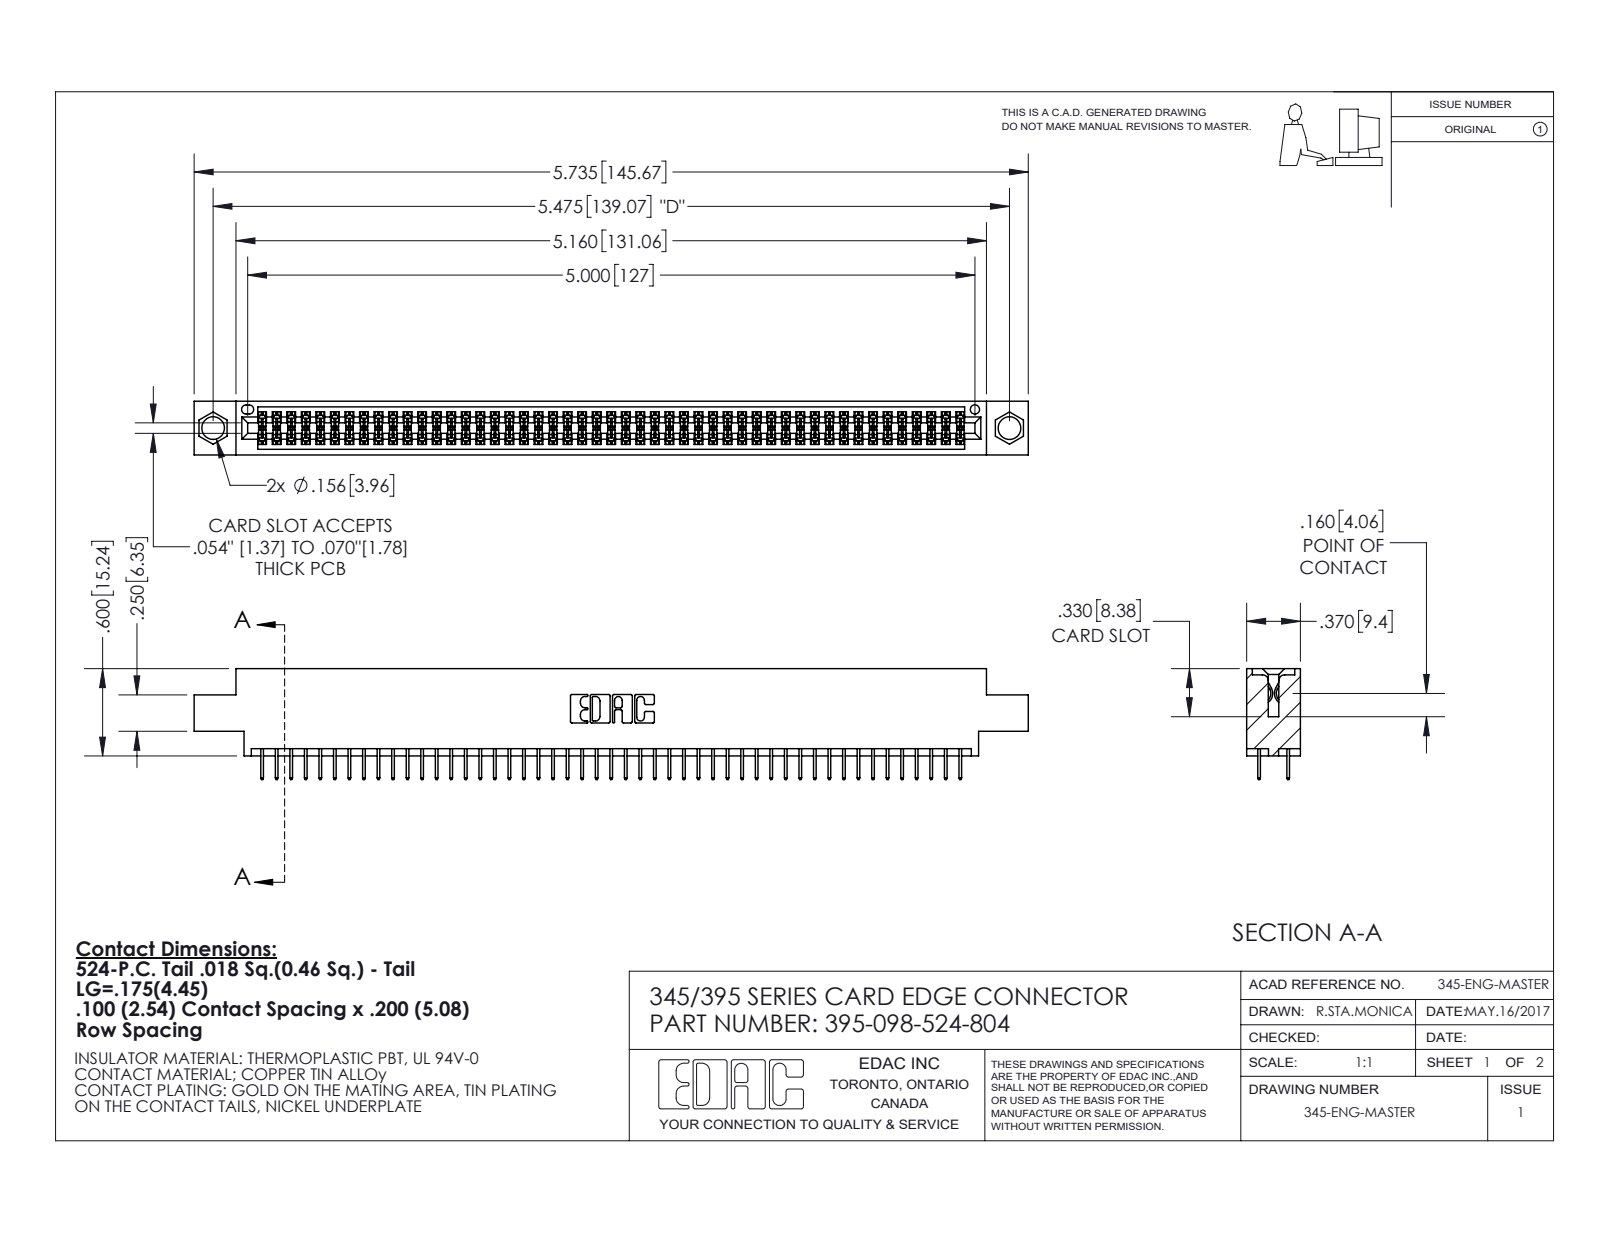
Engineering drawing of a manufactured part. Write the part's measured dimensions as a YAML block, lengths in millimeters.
part_name: "345-292-001_345-293-124; 345 Part_0.170 Offset - 0.156 Dia-TI; 395-098-524-804"
step_written_by: "SolidWorks 2020 (CONFIG_CONTROL_DESIGN)"
units: millimeters
bodies: {solids: 99, faces: 5436, planar: 3920, cylindrical: 1516, other: 0}
overall_size: [145.7, 19.4, 9.4]
volume: 13800
surface_area: 20210
round_holes:
  - {diameter: 4, count: 2}
  - {diameter: 1.6, count: 1}
partial_cylinders:
  - {radius: 0.2, count: 147}
  - {radius: 0.3, count: 22}
  - {radius: 0.2, count: 6}
  - {radius: 0.8, count: 6}
  - {radius: 0.7, count: 3}
  - {radius: 0.4, count: 2}
  - {radius: 0.5, count: 2}
  - {radius: 0.6, count: 2}
face_to_face_distances: [1.8, 7.6, 9.4, 5.1, 2.5, 6.9, 0.6, 5.7, 4.4, 1.8]
hole_center_spacings: [6.9, 133.1, 139.1]
